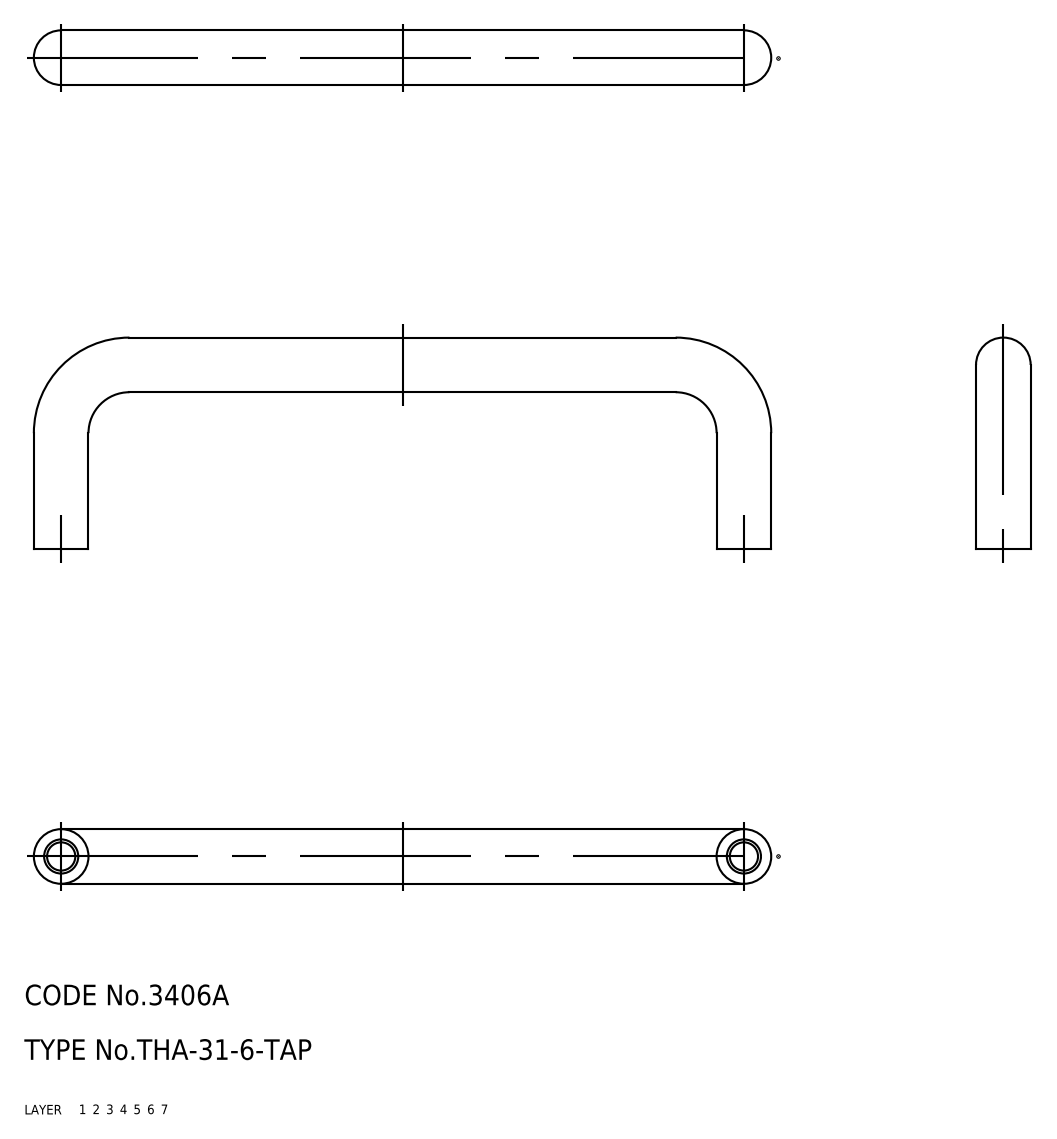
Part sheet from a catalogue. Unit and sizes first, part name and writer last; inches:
Units: inches
Overall size (bounding box): 4.252 × 1.22 × 0.315
Volume: 0.414 in³ · Surface area: 6.457 in²
Bodies: 1 solid, 18 faces (0 planar, 0 cylindrical, 18 other)
Part name (STEP PRODUCT): pull
STEP written by: CADfix (AUTOMOTIVE_DESIGN)
